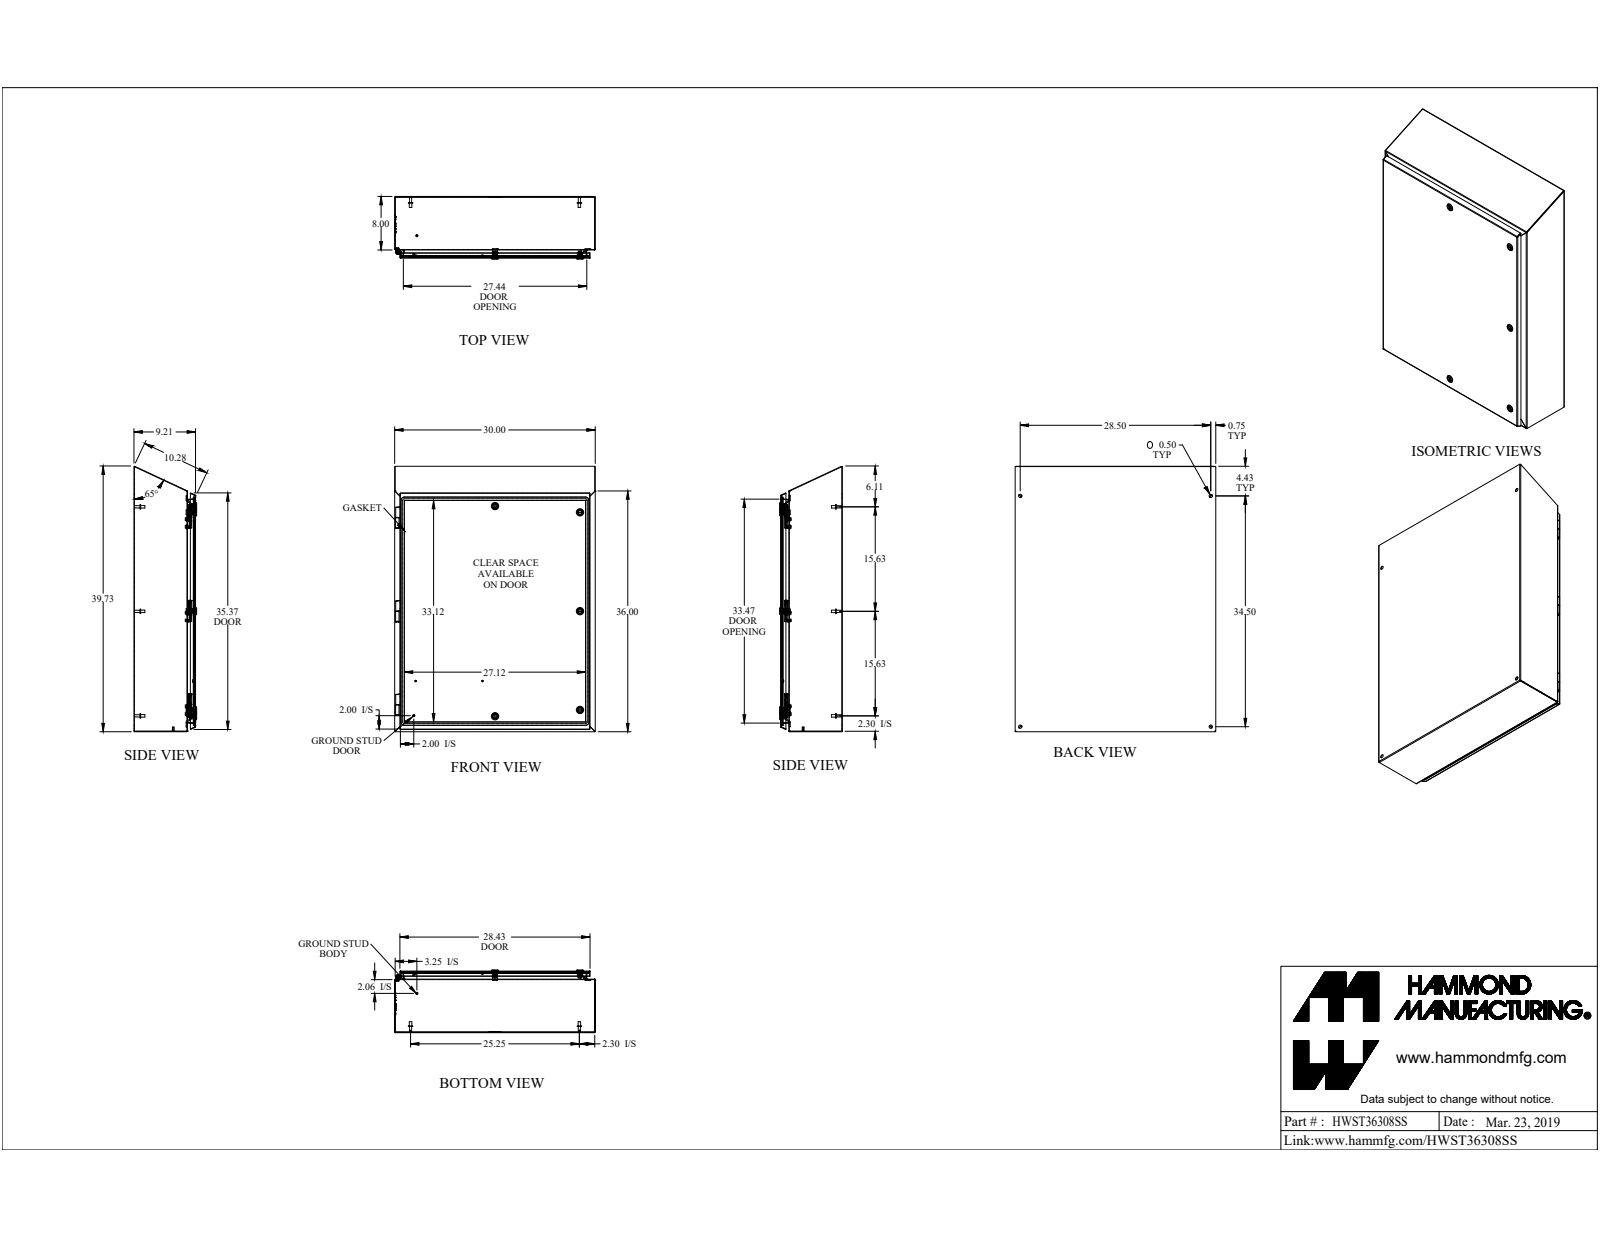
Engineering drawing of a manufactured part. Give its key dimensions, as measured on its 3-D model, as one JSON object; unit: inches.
{"part_name": "HWST36308S16", "step_written_by": "SolidWorks 2019 (AUTOMOTIVE_DESIGN)", "units": "inches", "bodies": {"solids": 69, "faces": 1564, "planar": 983, "cylindrical": 434, "other": 147}, "overall_size": [39.684, 30, 9.37], "volume_in3": 290, "surface_area_in2": 7885, "round_holes": [[0.5, 9], [0.194, 6], [0.194, 6], [0.24, 6], [0.275, 6], [0.197, 5], [0.387, 5], [0.63, 5], [0.768, 5], [0.13, 2], [0.24, 1], [3.5, 1]], "round_bosses_or_shafts": [[0.226, 12], [0.625, 11], [0.65, 6], [0.375, 6], [0.332, 6], [0.236, 6], [1.1, 5], [0.785, 5]], "partial_cylinders_radius": [[0.039, 24], [0.25, 24], [0.125, 22], [0.012, 16], [0.03, 16], [0.108, 16], [0.036, 12], [0.108, 9]], "face_to_face_distances": [0.072, 9.066, 9.138, 0.072, 9.138, 9.21, 29.928, 7.928, 29.856, 30], "hole_center_spacings": [1.142, 13.99, 13.989, 27.979, 12.848, 15.131, 12.75, 12.847]}
